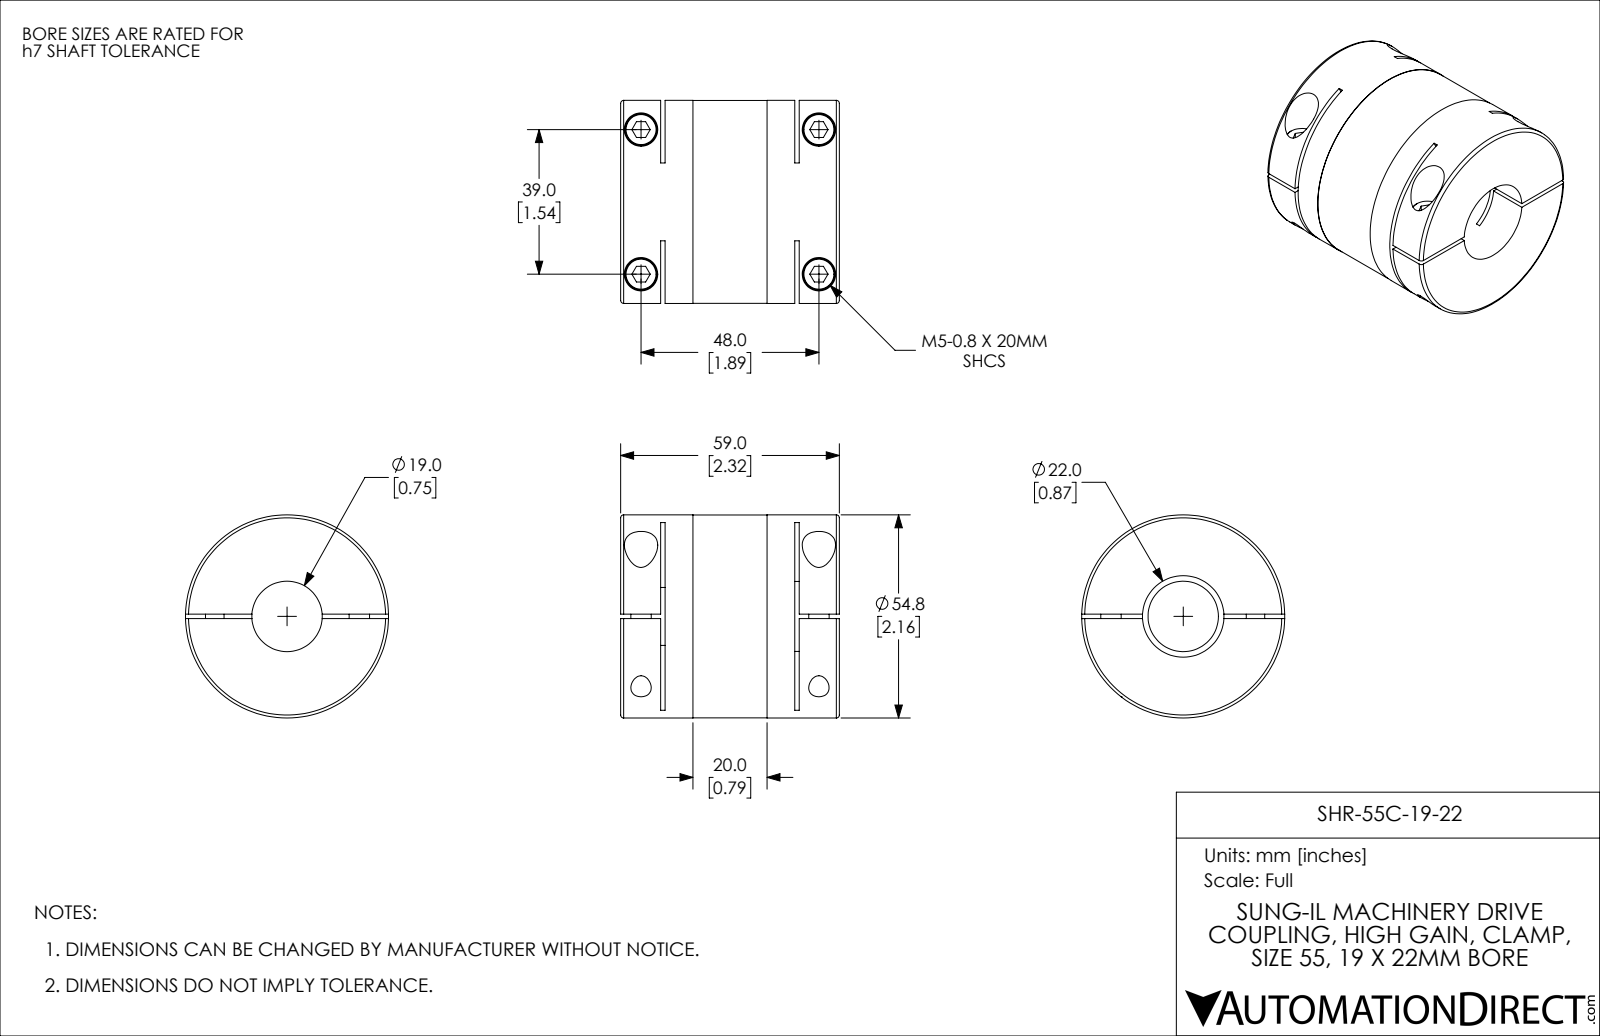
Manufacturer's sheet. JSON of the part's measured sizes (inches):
{"part_name": "SHR-55C-19-22", "step_written_by": "SolidWorks 2021 (CONFIG_CONTROL_DESIGN)", "units": "inches", "bodies": {"solids": 1, "faces": 144, "planar": 70, "cylindrical": 58, "other": 16}, "overall_size": [2.323, 2.157, 2.157], "volume_in3": 6.699, "surface_area_in2": 44.43, "round_holes": [[0.217, 4], [0.354, 4], [0.748, 1], [0.866, 1], [0.945, 1]], "round_bosses_or_shafts": [[0.335, 4], [0.197, 2], [2.157, 1], [2.154, 1]], "partial_cylinders_radius": [[2.362, 2]], "face_to_face_distances": [0.047, 0.472, 1.85, 0.425, 1.898, 1.425, 2.323, 1.378, 1.472, 0.768], "hole_center_spacings": [1.535, 1.89, 2.435]}
